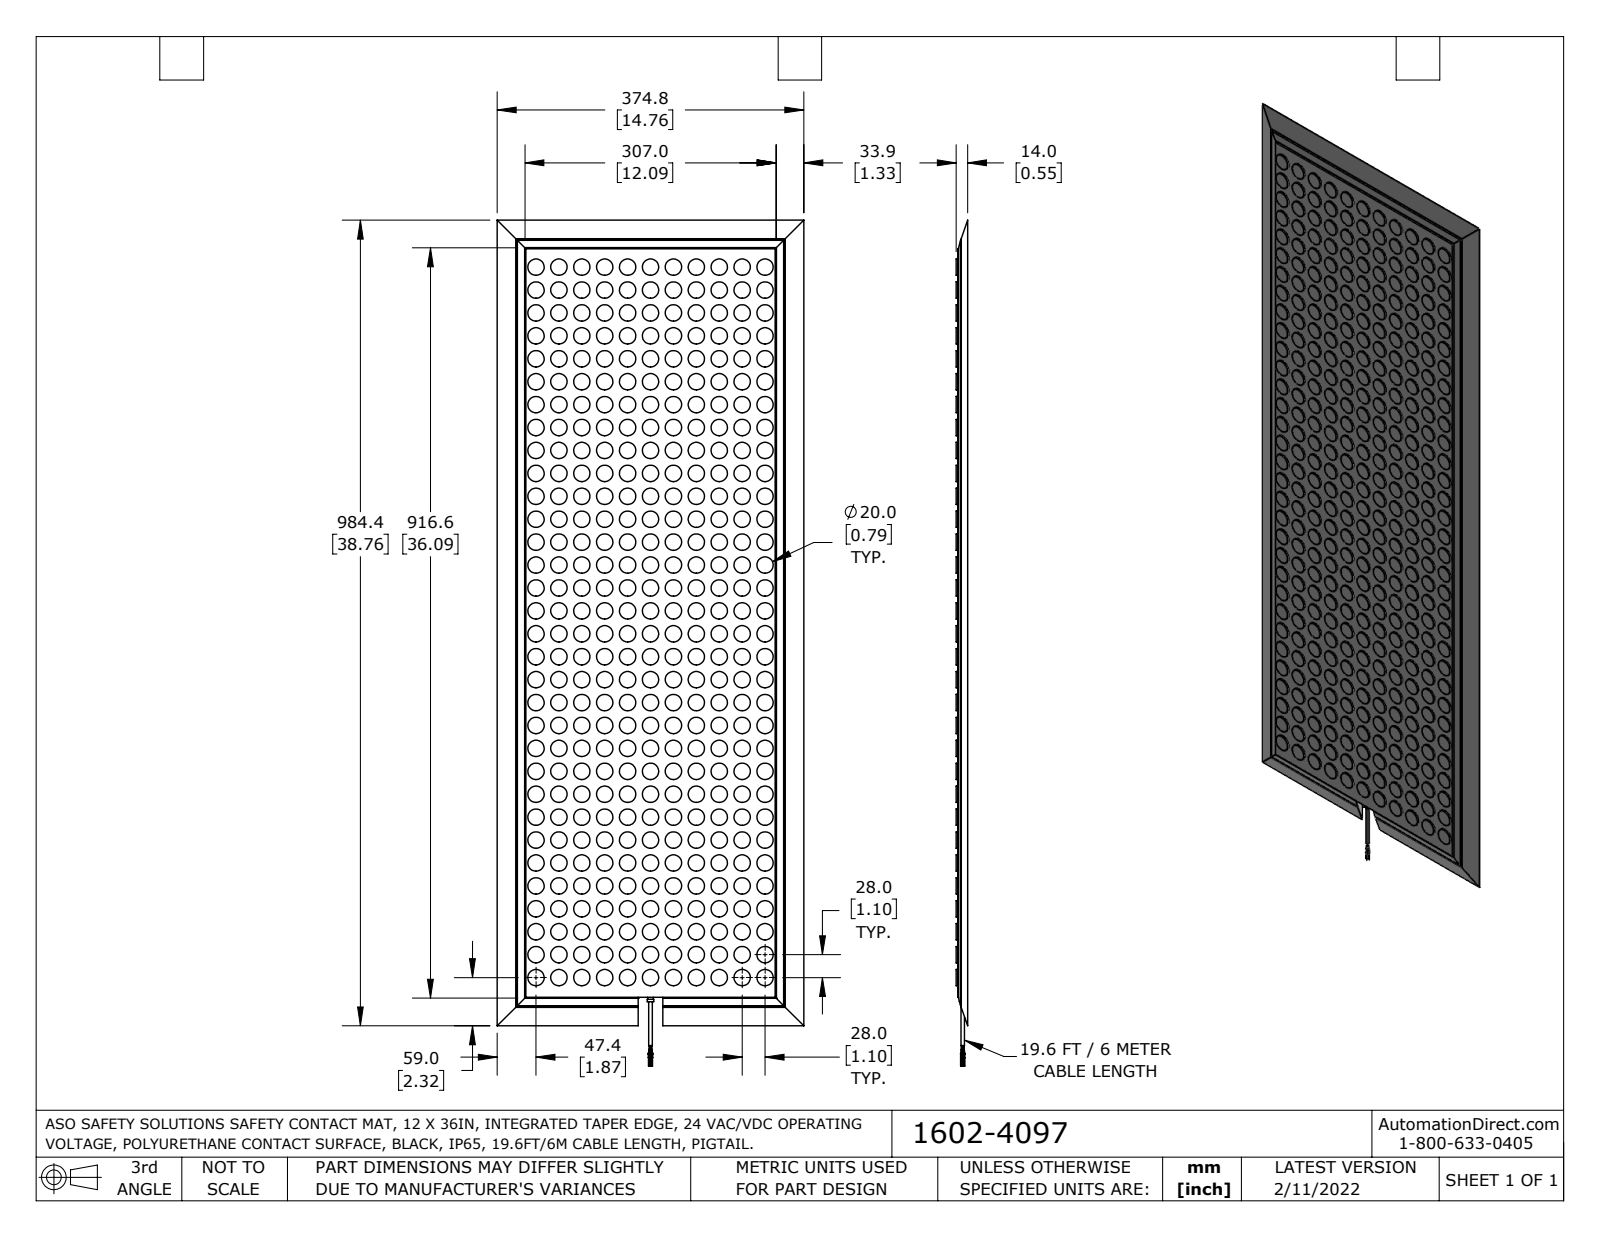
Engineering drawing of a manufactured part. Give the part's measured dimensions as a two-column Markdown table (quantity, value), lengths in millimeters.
| quantity | value |
| --- | --- |
| part name | 1602-4097_Default |
| STEP written by | SolidWorks 2021 (CONFIG_CONTROL_DESIGN) |
| units | millimeters |
| bodies | 3 solids, 1229 faces (410 planar, 787 cylindrical, 32 other) |
| overall size | 1033.4 × 374.8 × 14 |
| volume | 4 074 000 mm³ |
| surface area | 816 100 mm² |
| round holes (diameter × count) | 4.4 × 1 |
| round bosses / shafts (diameter × count) | 20 × 352, 1.2 × 20, 0.8 × 8, 8 × 1, 7 × 1 |
| partial cylindrical surfaces (radius × count) | 0.2 × 4 |
| main face-to-face distances | 12, 14, 2, 304.8, 6, 8, 914.4, 137.4, 167.4, 30 |
